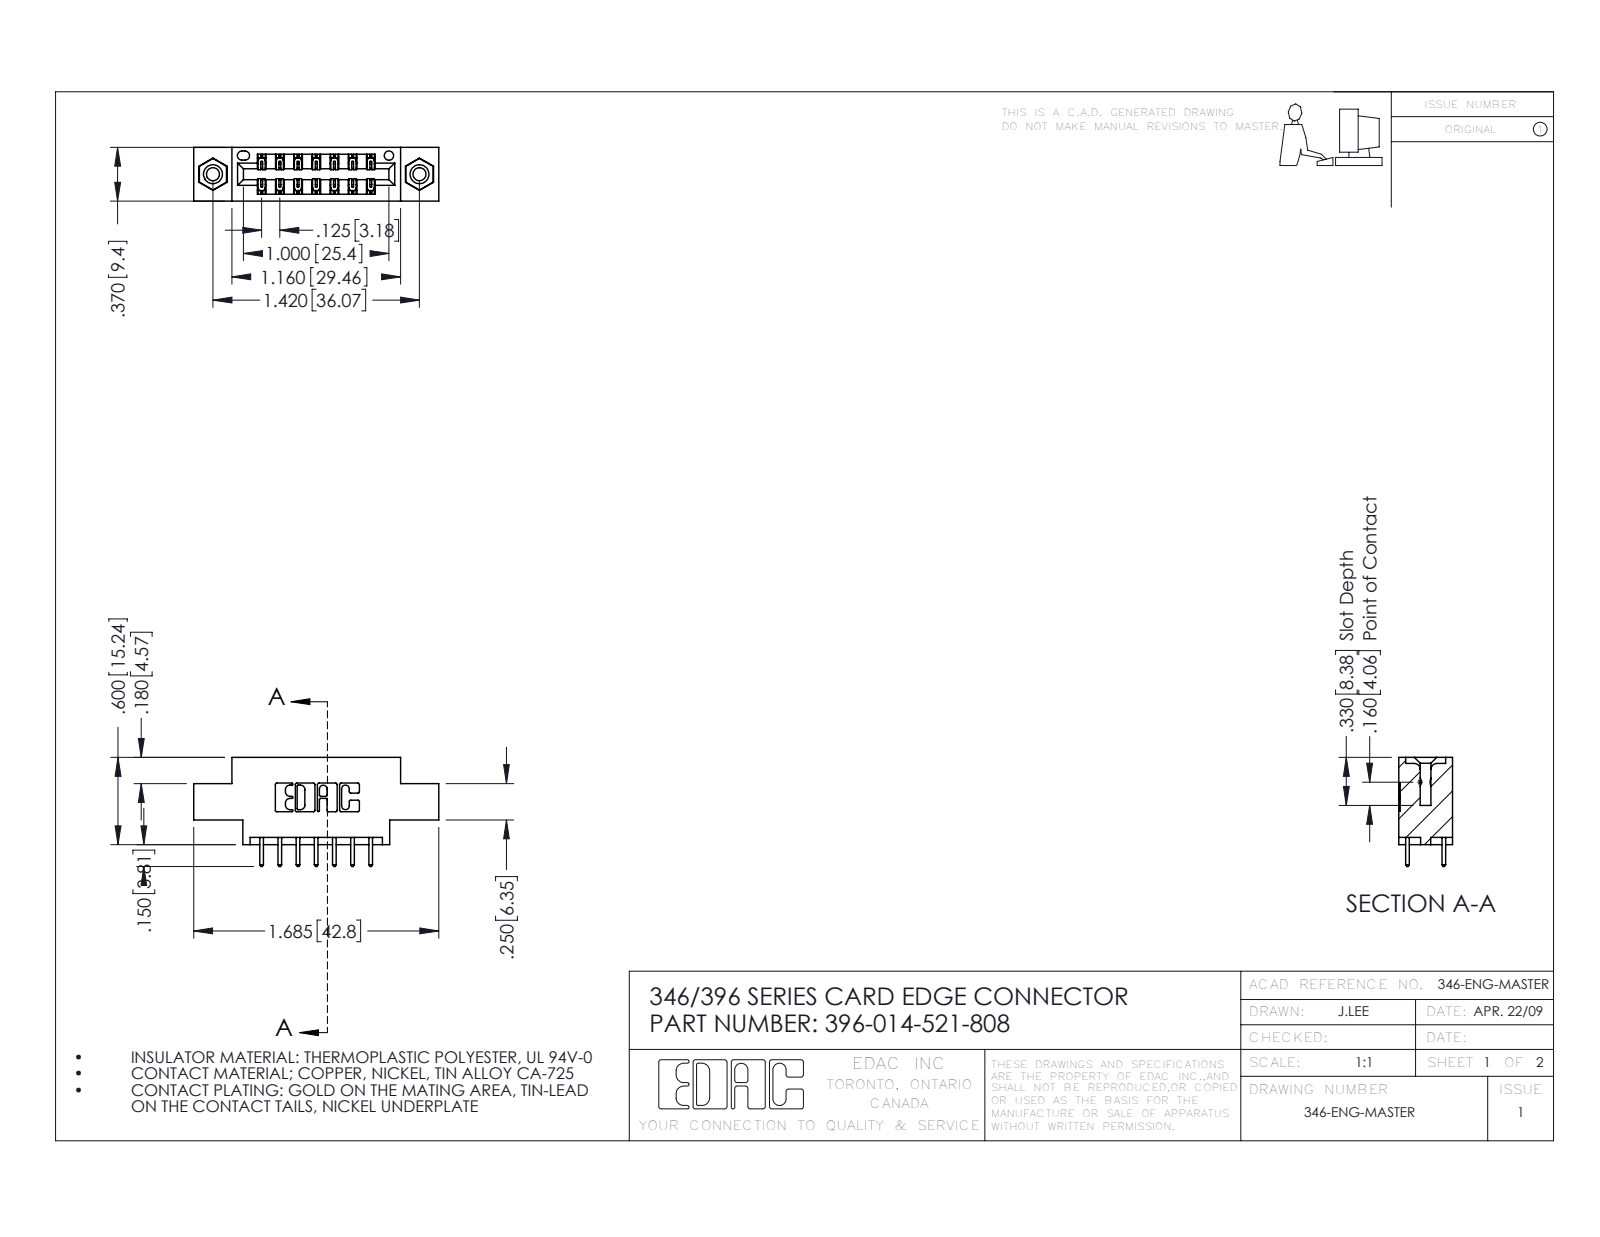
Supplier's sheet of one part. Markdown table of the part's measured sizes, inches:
| quantity | value |
| --- | --- |
| part name | 345-250-001_345-250-003-102; 396-014-521-808; 346 Part_0.170 Offset - 0.156 Dia-TI; 345-292-001_345-293-121 |
| STEP written by | SolidWorks 2016 (CONFIG_CONTROL_DESIGN) |
| units | inches |
| bodies | 17 solids, 914 faces (602 planar, 296 cylindrical, 16 other) |
| overall size | 1.685 × 0.75 × 0.37 |
| volume | 0.228 in³ |
| surface area | 7.354 in² |
| round holes (diameter × count) | 0.089 × 2, 0.125 × 2, 0.156 × 2, 0.064 × 1 |
| round bosses / shafts (diameter × count) | 0.155 × 2 |
| partial cylindrical surfaces (radius × count) | 0.01 × 22, 0.006 × 21, 0.01 × 14, 0.007 × 6, 0.031 × 6, 0.026 × 3, 0.014 × 2, 0.022 × 2 |
| main face-to-face distances | 0.25, 0.37, 0.048, 0.322, 0.222, 0.072, 0.298, 0.025, 0.148, 0.275 |
| hole center spacings | 0.246, 1.217, 1.42 |
